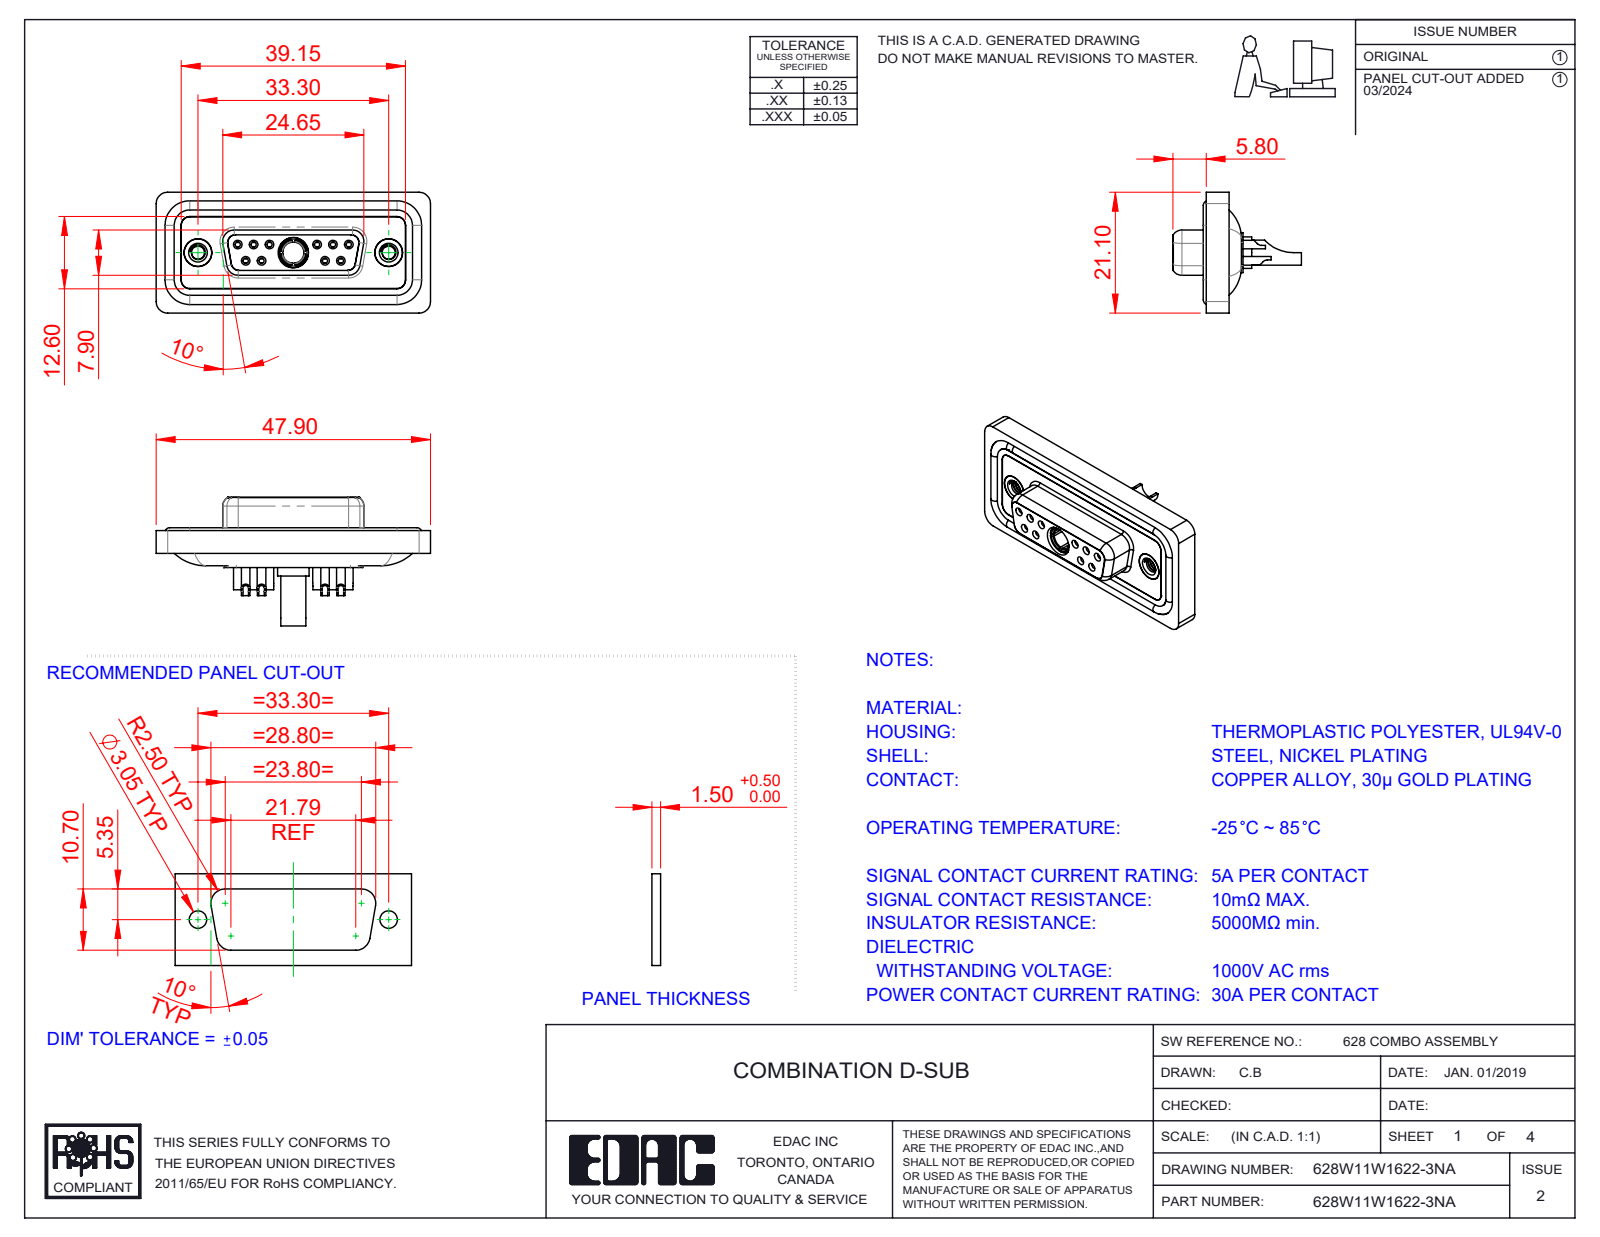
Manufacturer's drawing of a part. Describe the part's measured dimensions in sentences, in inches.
The part is named "628Combo Contact Row 1_22; 628W11W1622-3NA; 628Combo Shell Front_15 Contacts; 628Combo Waterproof Housing_15 Contacts (+5 more)". Its 3-D file was written by "SolidWorks 2023 (CONFIG_CONTROL_DESIGN)". It is 19 solids with 1014 faces: 307 planar, 426 cylindrical and 281 other. Overall it measures 1.886 by 0.884 by 0.831 inches. Its volume is 0.377 cubic inches and its surface area 15.87 square inches. Round holes: 10 of diameter 0.035, 10 of diameter 0.039, 10 of diameter 0.043, 10 of diameter 0.059, 10 of diameter 0.079, 6 of diameter 0.067, 4 of diameter 0.063, 3 of diameter 0.191, 2 of diameter 0.089, 2 of diameter 0.157, 2 of diameter 0.159, 2 of diameter 0.197. Round bosses or shafts: 10 of diameter 0.087, 10 of diameter 0.063, 2 of diameter 0.195, 2 of diameter 0.189, 1 of diameter 0.217, 1 of diameter 0.205, 1 of diameter 0.195, 1 of diameter 0.187. Partial cylindrical surfaces (rounded edges, fillets, slot ends): 22 of radius 0.059, 20 of radius 0.079, 12 of radius 0.053, 8 of radius 0.063, 6 of radius 0.039, 4 of radius 0.01, 4 of radius 0.02, 4 of radius 0.024. The main face-to-face distances are 0.016, 0.063, 0.071, 0.114, 0.02, 0.043, 0.222, 0.293, 0.26, 0.278. The hole center spacings are 0.124, 0.109, 0.545, 0.436, 0.654, 0.198, 0.198, 0.218.
